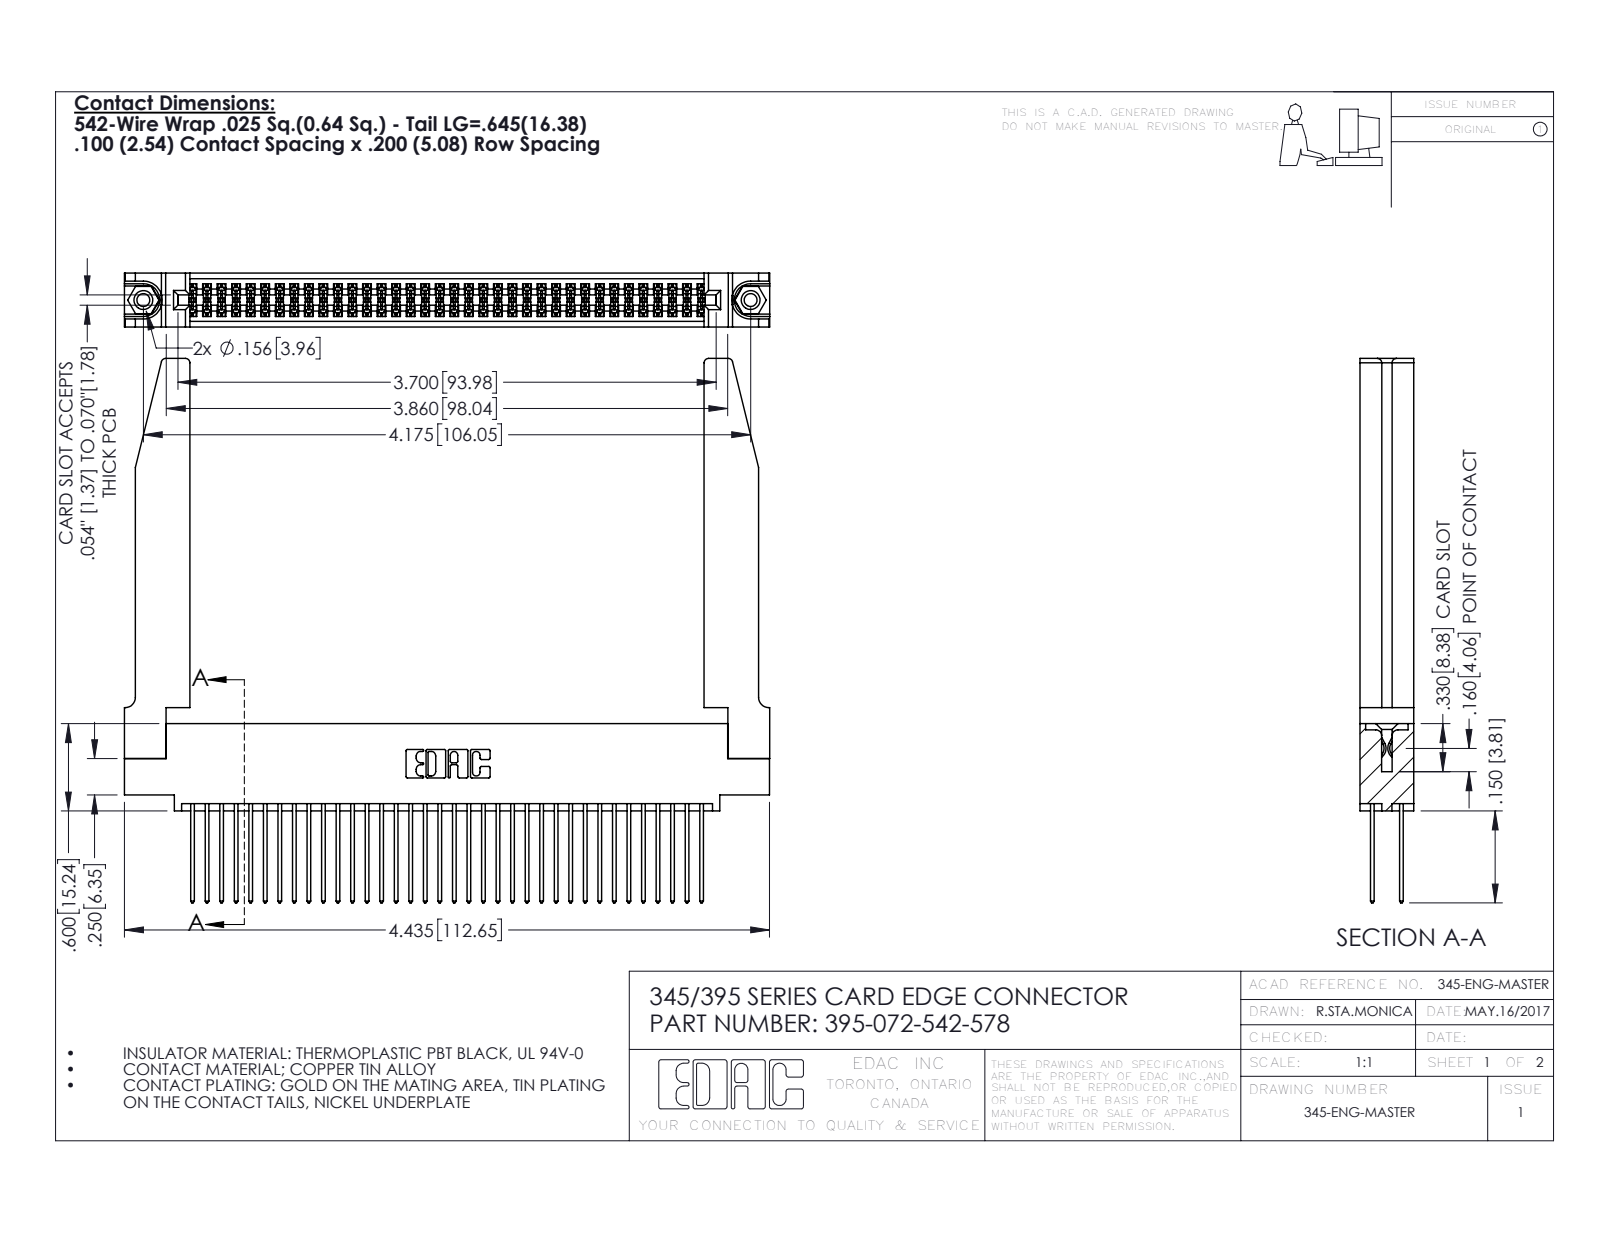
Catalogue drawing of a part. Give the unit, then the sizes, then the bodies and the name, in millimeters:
Units: millimetres
Overall size (bounding box): 112.7 × 95 × 9.4
Round holes (diameter × count): ⌀2.3 ×2, ⌀3.2 ×2, ⌀4 ×2, ⌀1.6 ×1
Round bosses / shafts (diameter × count): ⌀3.9 ×2
Partial cylindrical surfaces — rounded edges, fillets, slot ends (radius × count): R0.2 ×108, R0.3 ×72, R0.3 ×22, R0.8 ×8, R0.2 ×6, R0.8 ×6, R0.7 ×3, R0.4 ×2
Main face-to-face distances: 1.8, 7.6, 9.4, 5.1, 2.5, 6.9, 0.6, 5.7, 4.4, 3.8
Hole centre spacings: 6.9, 100.1, 106
Volume: 18 930 mm³ · Surface area: 24 870 mm²
Bodies: 77 solids, 3964 faces (2602 planar, 1310 cylindrical, 52 other)
Part name (STEP PRODUCT): 345-292-001_345-293-142; 395-072-542-578; 345-250-001_345-250-001-102; 345-220-078_345-220-078 (+1 more)
STEP written by: SolidWorks 2016 (CONFIG_CONTROL_DESIGN)
